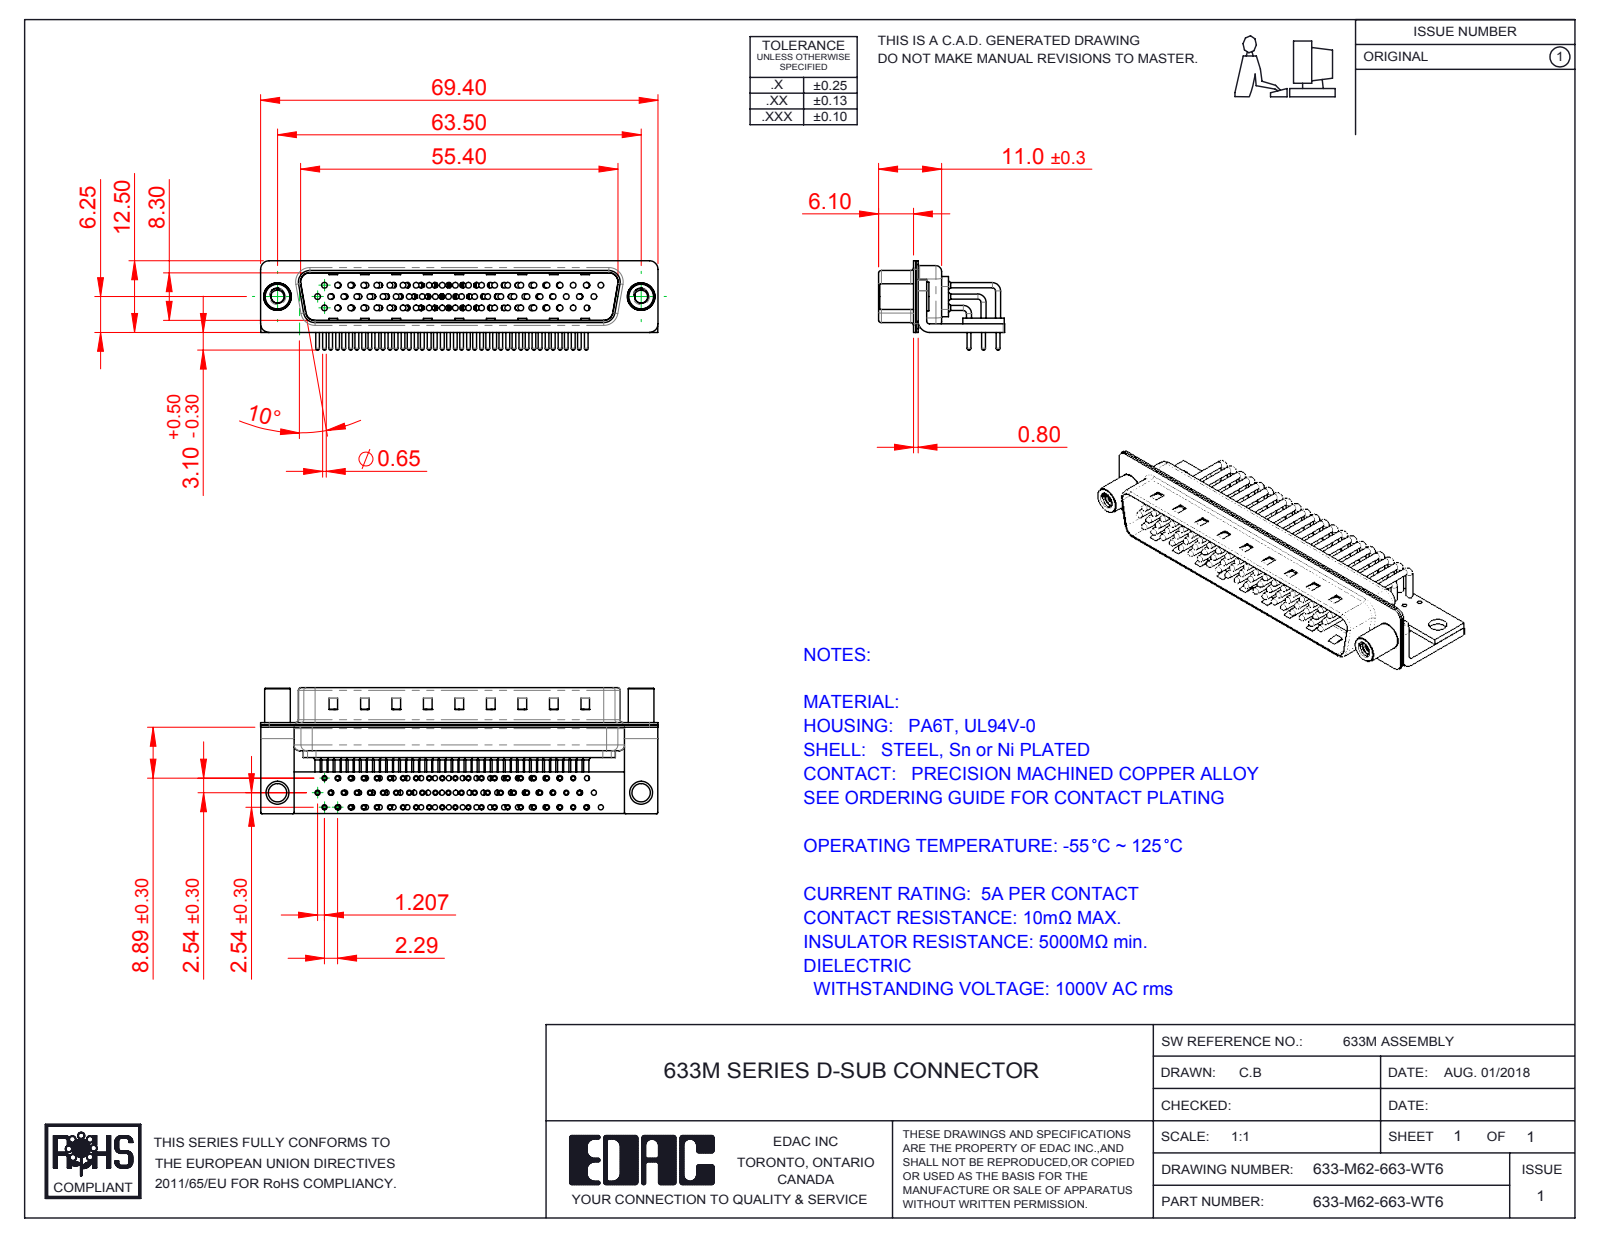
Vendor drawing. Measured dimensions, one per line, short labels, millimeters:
name: 633M Contact Row 1; 633M Stabilizer Bracket; 633M Contact Row 3; 633M Stabilizer Board_62 Contacts (+6 more)
written by: SolidWorks 2016 (CONFIG_CONTROL_DESIGN)
unit: mm
bodies: 70 solids, 7456 faces (4199 planar, 2561 cylindrical, 696 other)
size: 69.4 × 22 × 15.6
volume: 5 201 mm³; area: 15 819 mm²
holes: 62× ⌀0.9, 62× ⌀1, 62× ⌀1.7, 62× ⌀2, 2× ⌀2.26, 2× ⌀3.2, 2× ⌀4, 2× ⌀4.8
bosses: 118× ⌀0.9, 62× ⌀1.5, 62× ⌀0.65, 56× ⌀1, 2× ⌀5, 2× ⌀4.9, 2× ⌀4.5
rounds: 62× R1.01, 16× R0.25, 16× R1.5, 13× R2, 9× R0.5, 8× R1.6, 4× R0.6, 4× R0.65
face distances: 0.4, 0.85, 1.25, 1.5, 9.55, 1, 1.9, 10.4, 8.3, 0.8
hole spacings: 7.24, 2.41, 9.65, 4.83, 14.48, 16.89, 2.81, 2.32
